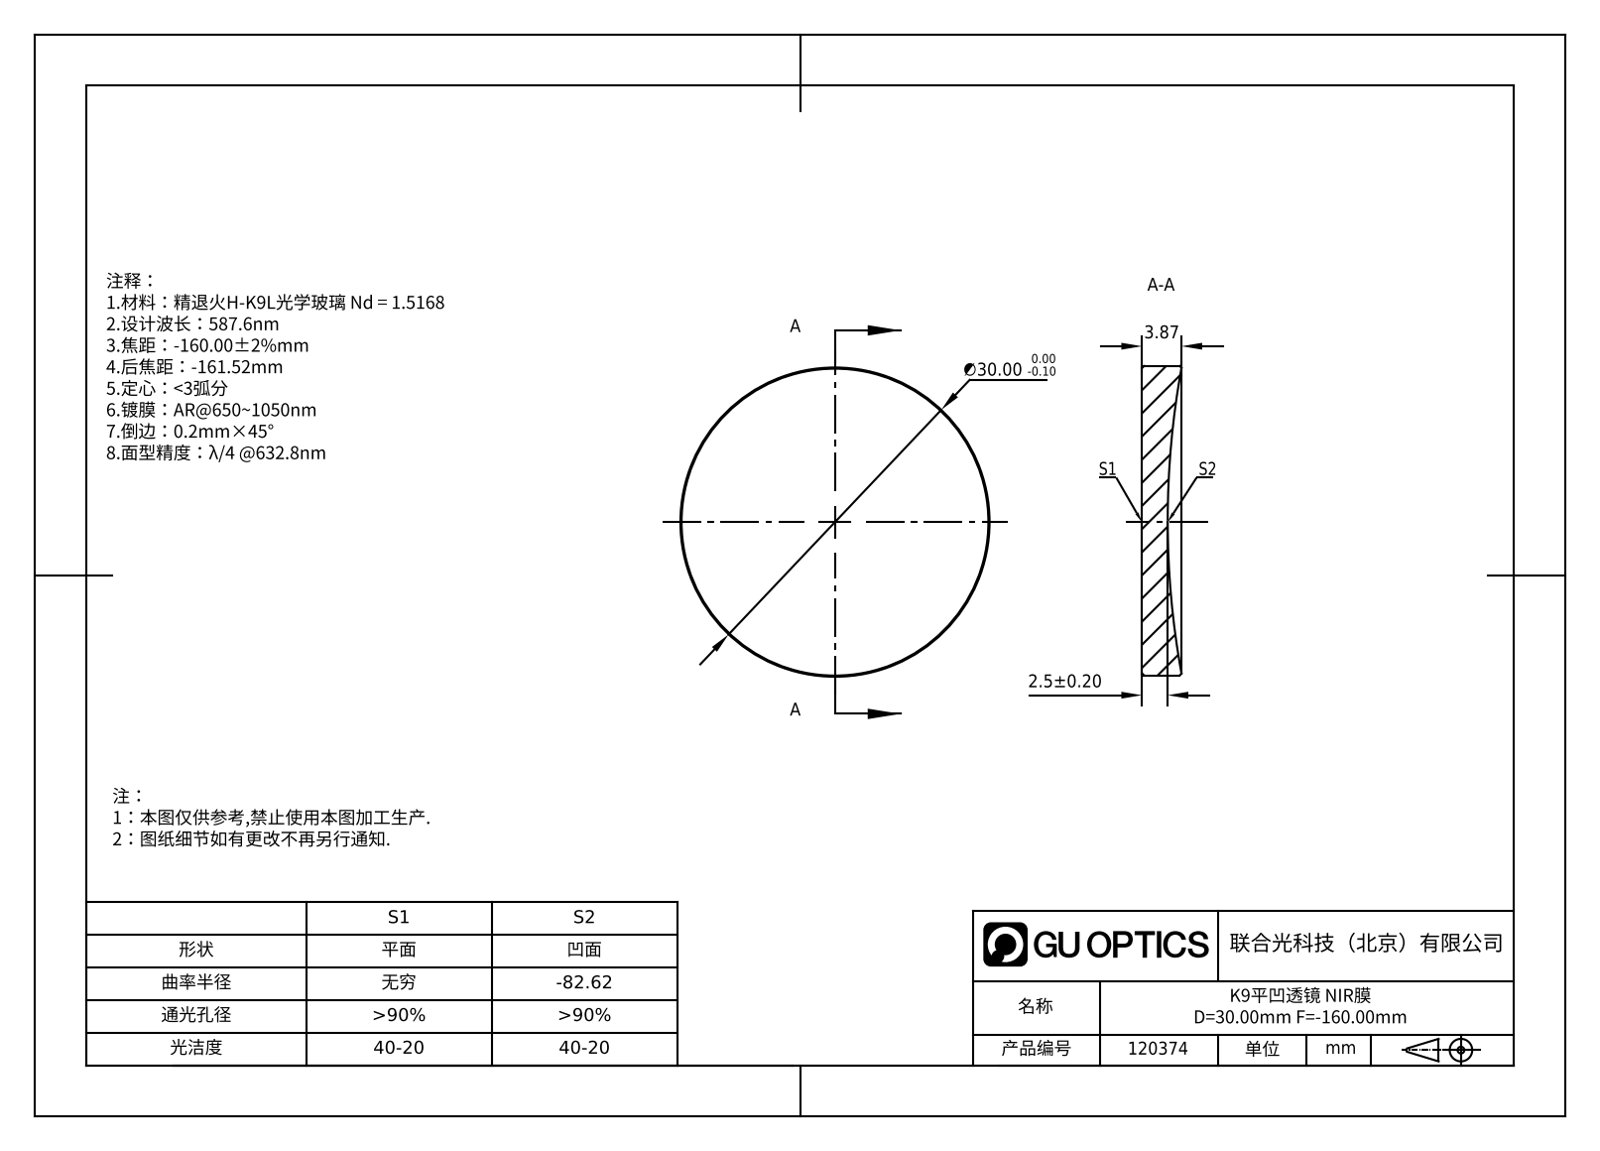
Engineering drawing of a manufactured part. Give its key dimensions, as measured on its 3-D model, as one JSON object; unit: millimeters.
{"part_name": "GL13-030-160", "step_written_by": "SolidWorks 2022 (AUTOMOTIVE_DESIGN)", "units": "millimeters", "bodies": {"solids": 1, "faces": 9, "planar": 1, "cylindrical": 2, "other": 6}, "overall_size": [30, 30, 3.84], "volume_mm3": 2246, "surface_area_mm2": 1761, "round_bosses_or_shafts": [[30, 1]]}
